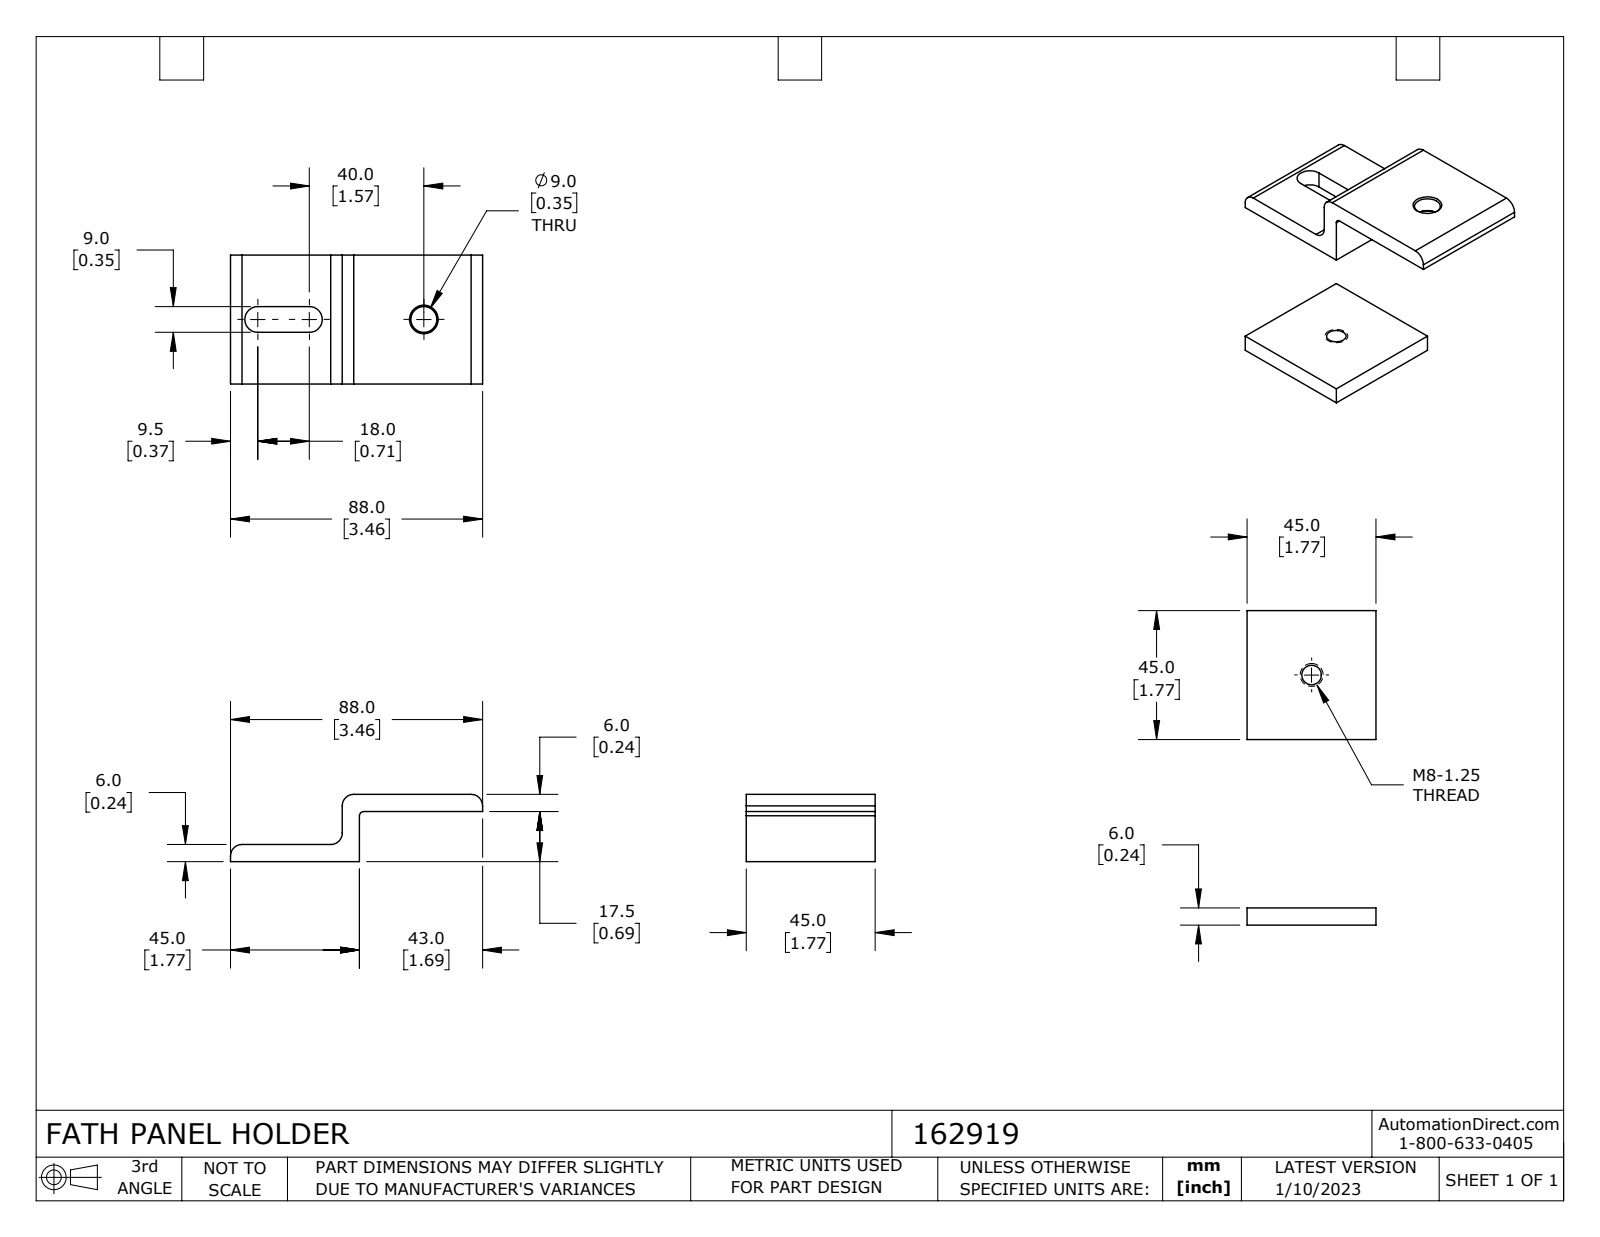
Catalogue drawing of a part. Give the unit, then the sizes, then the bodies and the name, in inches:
Units: inches
Overall size (bounding box): 3.465 × 3.327 × 1.772
Round holes (diameter × count): ⌀0.268 ×1, ⌀0.354 ×1
Partial cylindrical surfaces — rounded edges, fillets, slot ends (radius × count): R0.157 ×4, R0.177 ×2, R0.059 ×1
Main face-to-face distances: 0.236, 3.091, 2.402, 0.689, 2.165, 2.854, 0.925, 3.327, 1.772, 0.453
Hole centre spacings: 1.772
Volume: 2.343 in³ · Surface area: 24.95 in²
Bodies: 2 solids, 33 faces (18 planar, 11 cylindrical, 4 other)
Part name (STEP PRODUCT): 162919
STEP written by: SolidWorks 2021 (CONFIG_CONTROL_DESIGN)
